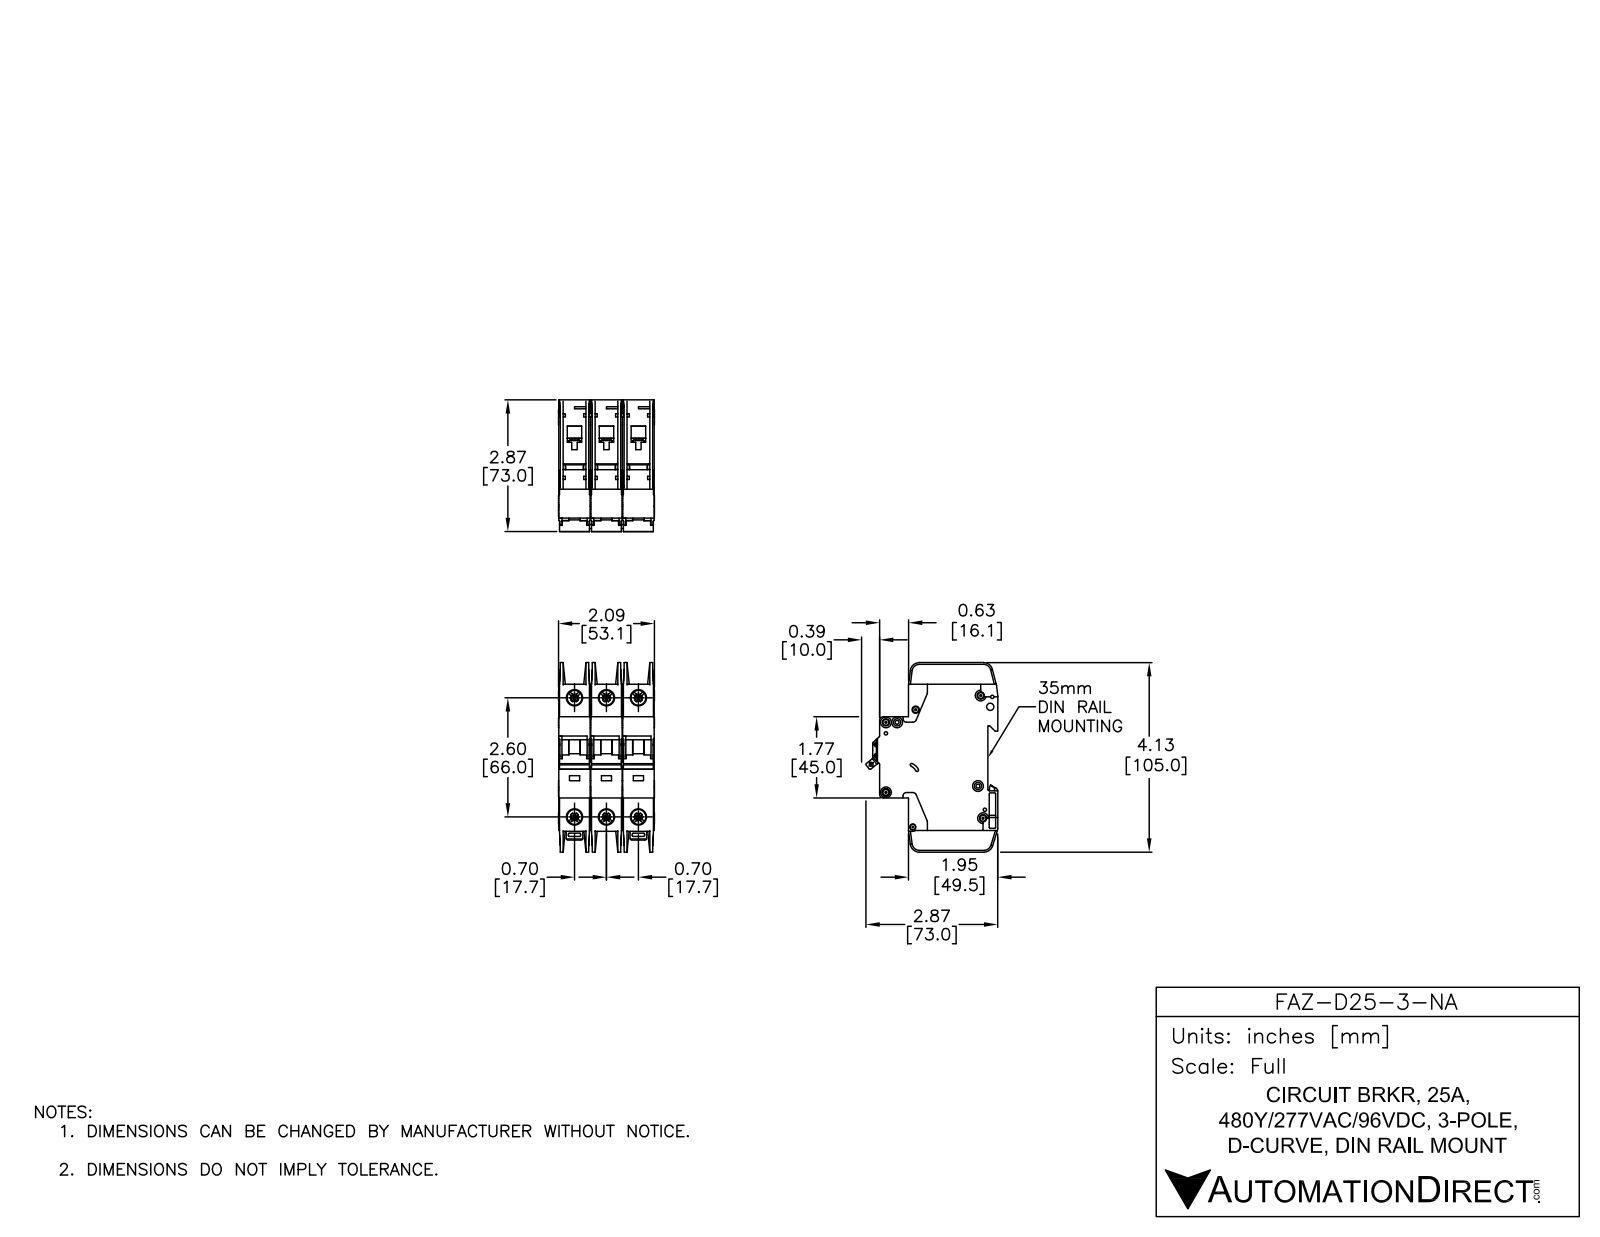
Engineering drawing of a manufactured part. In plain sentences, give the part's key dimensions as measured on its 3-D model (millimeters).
The part is named "FAZ-D25-3-NA". Its 3-D file was written by "SolidWorks 2014 (AUTOMOTIVE_DESIGN)". It is 9 solids with 2352 faces: 1227 planar, 789 cylindrical and 336 other. Overall it measures 105 by 73.04 by 53.1 millimeters. Its volume is 233 085 cubic millimeters and its surface area 74 219 square millimeters. Round holes: 7 of diameter 3.6, 6 of diameter 7.15, 6 of diameter 8.2, 2 of diameter 1.09, 2 of diameter 1.5, 2 of diameter 4, 1 of diameter 1.9, 1 of diameter 2.15, 1 of diameter 2.2, 1 of diameter 2.55, 1 of diameter 3.3, 1 of diameter 3.4. Round bosses or shafts: 7 of diameter 6, 3 of diameter 2.5. Partial cylindrical surfaces (rounded edges, fillets, slot ends): 65 of radius 0.25, 30 of radius 0.5, 26 of radius 1, 14 of radius 2, 5 of radius 1.8, 5 of radius 5, 4 of radius 4, 2 of radius 0.2. The main face-to-face distances are 17.7, 35.4, 17.5, 35.2, 0.7, 15.05, 2.45, 1.75, 15.75, 13.3. The hole center spacings are 17.7, 68.33, 66, 6.2, 35.4, 74.89, 5.19, 6.1.
